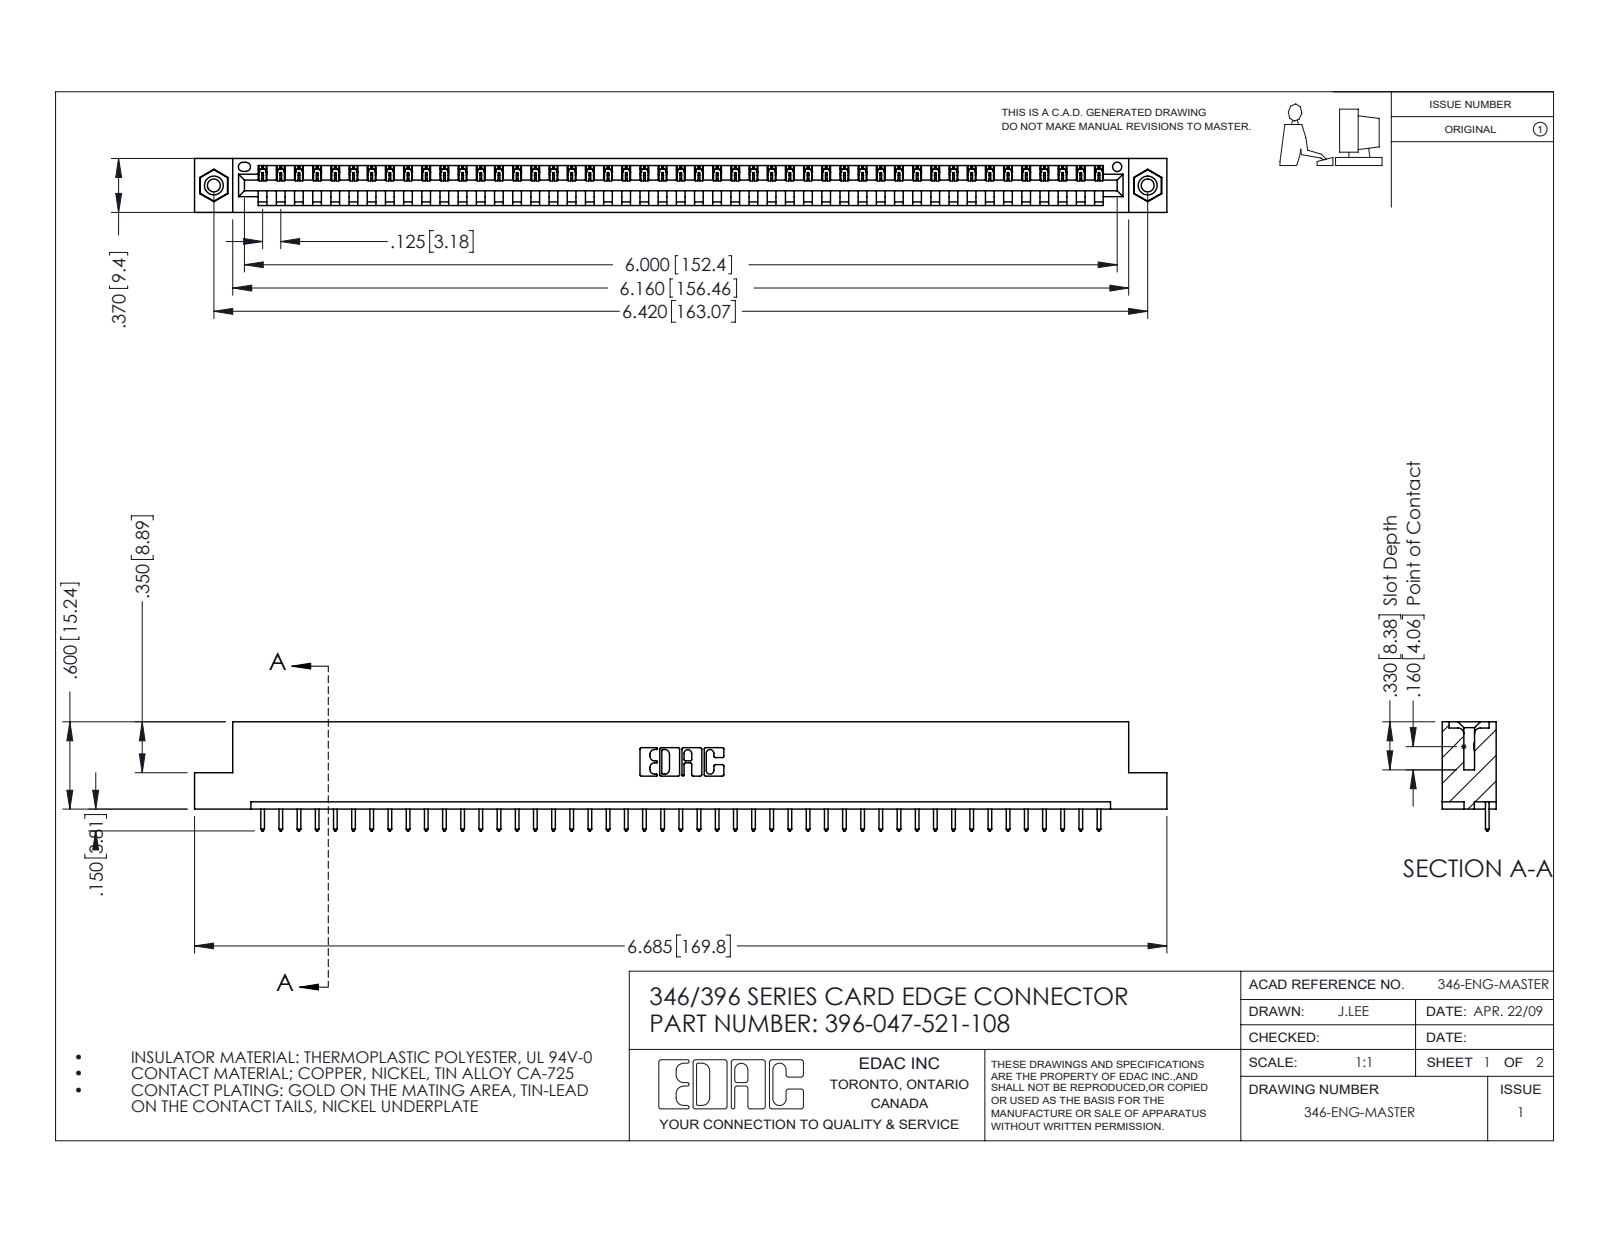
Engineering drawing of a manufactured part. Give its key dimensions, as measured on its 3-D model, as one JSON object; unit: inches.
{"part_name": "345-292-001_345-293-121; 396-047-521-108; 345-250-001_345-250-003-102; 346 Part_Flush Mounting Lugs - 0.156 Dia-TI", "step_written_by": "SolidWorks 2016 (CONFIG_CONTROL_DESIGN)", "units": "inches", "bodies": {"solids": 50, "faces": 2908, "planar": 1988, "cylindrical": 904, "other": 16}, "overall_size": [6.685, 0.75, 0.37], "volume_in3": 0.985, "surface_area_in2": 30.58, "round_holes": [[0.089, 2], [0.125, 2], [0.156, 2], [0.064, 1]], "round_bosses_or_shafts": [[0.155, 2]], "partial_cylinders_radius": [[0.006, 94], [0.01, 94], [0.01, 22], [0.007, 6], [0.031, 6], [0.026, 3], [0.031, 2], [0.04, 2]], "face_to_face_distances": [0.048, 0.322, 0.37, 0.25, 0.072, 0.298, 0.025, 0.148, 0.222, 0.1], "hole_center_spacings": [0.246, 6.211, 6.42]}
